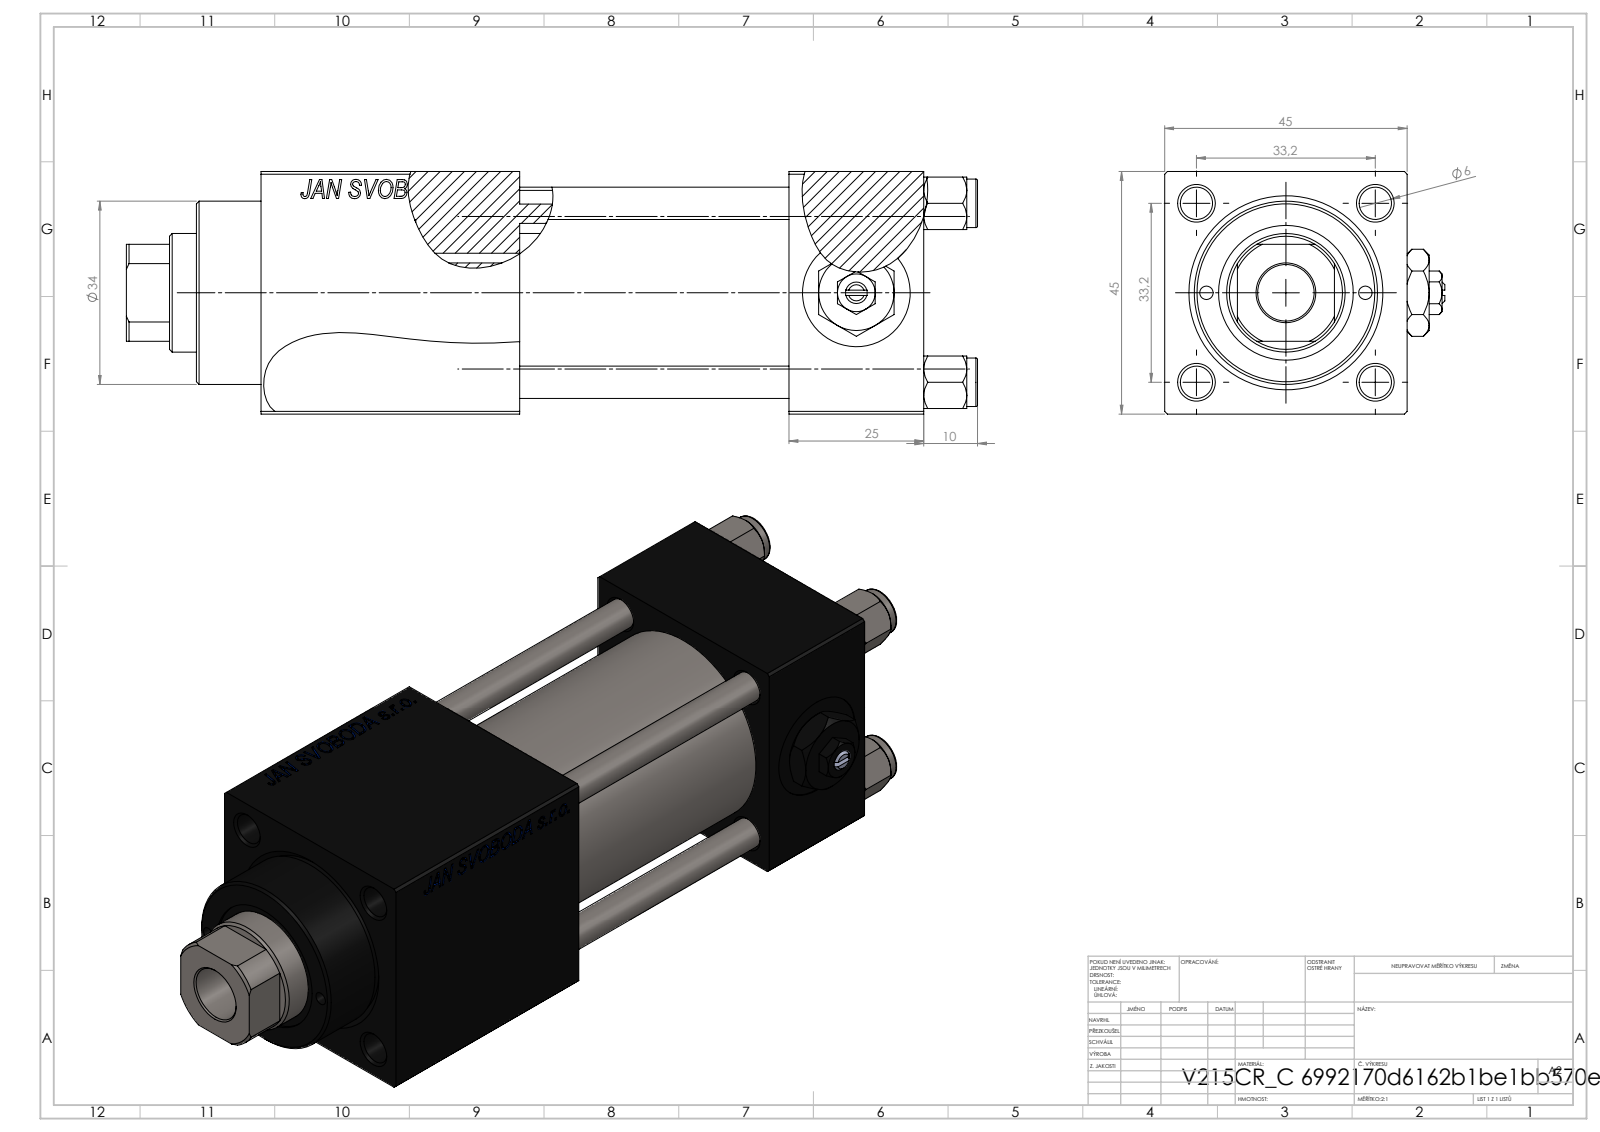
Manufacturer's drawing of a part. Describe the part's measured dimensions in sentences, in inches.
The part is named "V215CR_C_TYCINKA; V215_VC_A; Zatka_pro_OIL_PORT; V215CR_C_Body (+2 more)". Its 3-D file was written by "SolidWorks 2019 (CONFIG_CONTROL_DESIGN)". It is 12 solids with 1206 faces: 550 planar, 98 cylindrical and 558 other. Overall it measures 6.22 by 2.047 by 1.772 inches. Its volume is 12.74 cubic inches and its surface area 112.6 square inches. Round holes: 4 of diameter 0.236, 2 of diameter 0.098, 2 of diameter 0.276, 2 of diameter 0.518, 2 of diameter 0.787, 1 of diameter 0.413, 1 of diameter 0.866, 1 of diameter 0.945, 1 of diameter 0.984, 1 of diameter 1.26, 1 of diameter 1.299. Round bosses or shafts: 4 of diameter 0.354, 1 of diameter 1.496, 1 of diameter 1.339. Partial cylindrical surfaces (rounded edges, fillets, slot ends): 1 of radius 0.413. The main face-to-face distances are 1.772, 0.984, 1.969, 4.843, 2.953, 3.858, 1.89, 3.713, 2.728, 0.76. The hole center spacings are 0.657, 0.924, 1.307, 1.396, 0.581, 1.848, 1.161, 2.972.
